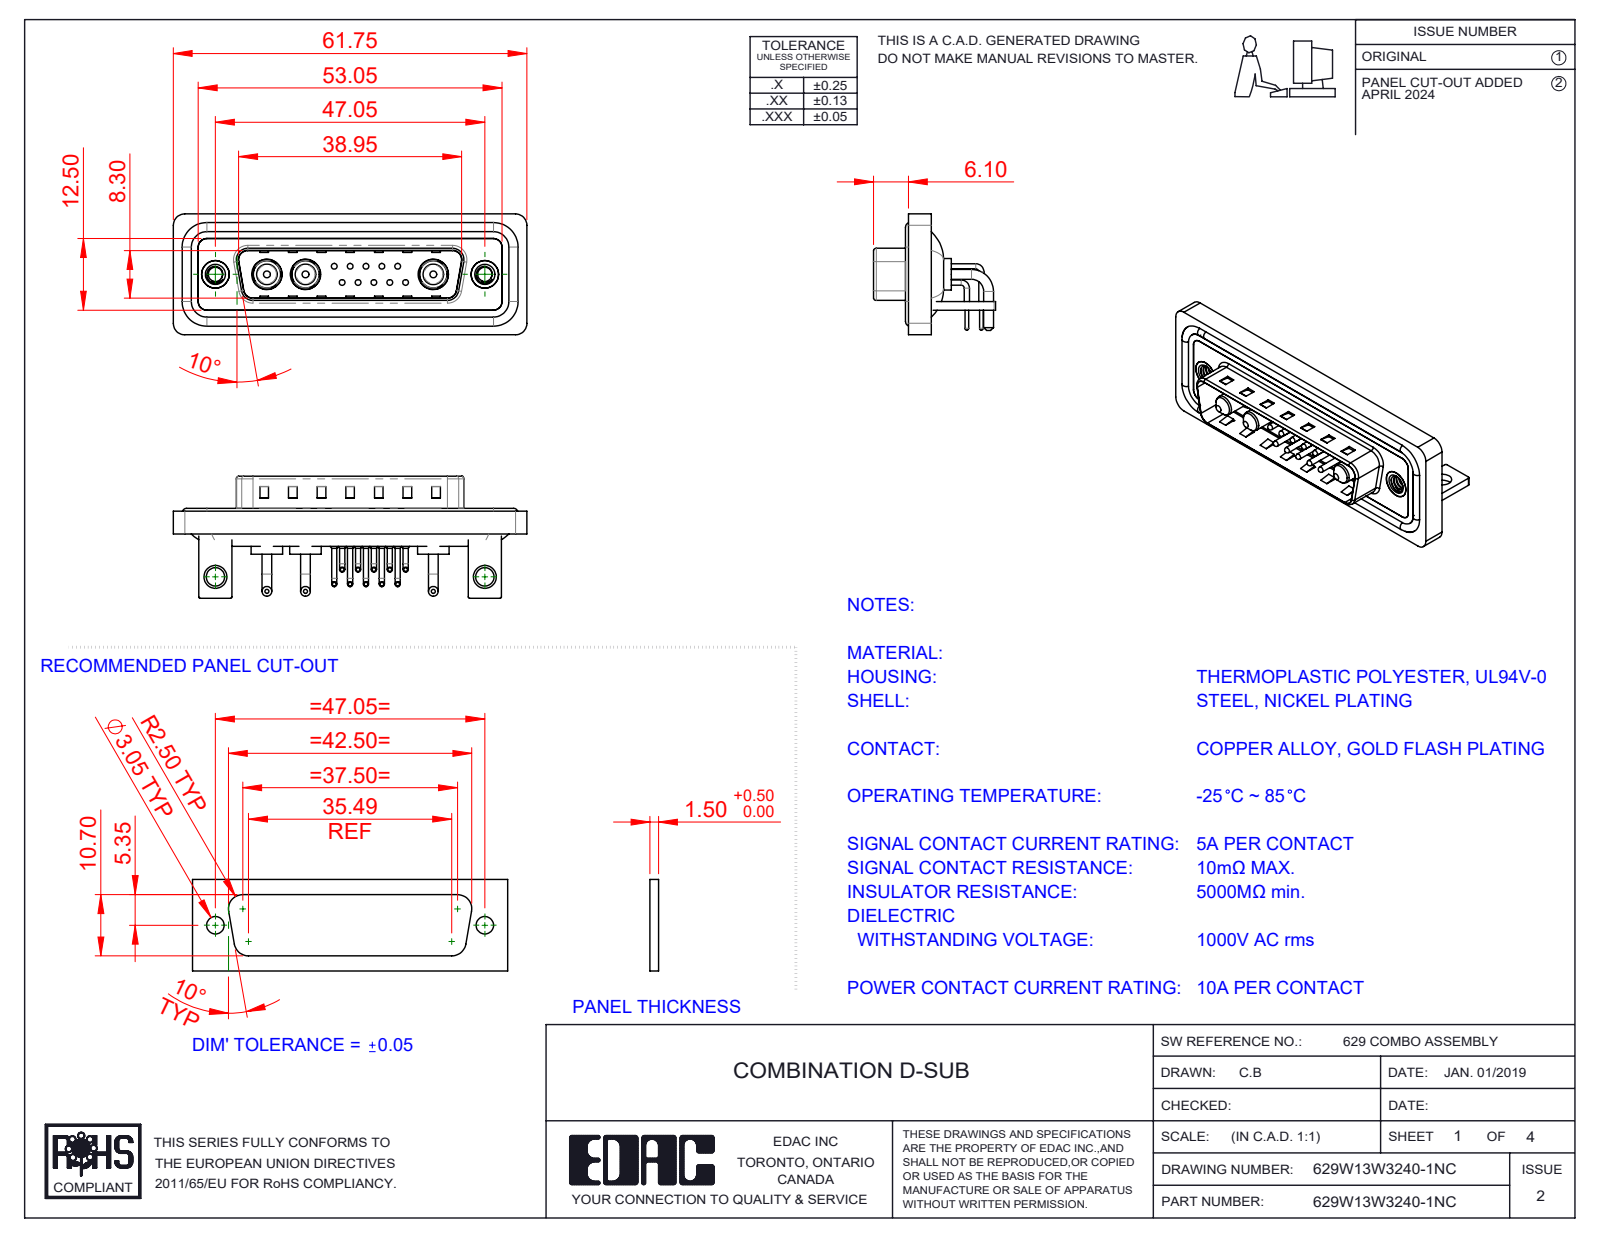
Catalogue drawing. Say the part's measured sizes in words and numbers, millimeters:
The part is named "629Combo Housing_13W3; 629Combo Contact Row 1; 629W13W3240-1NC; 629Combo Stabilizer Bracket (+6 more)". Its 3-D file was written by "SolidWorks 2023 (CONFIG_CONTROL_DESIGN)". It is 25 solids with 1750 faces: 899 planar, 629 cylindrical and 222 other. Overall it measures 61.75 by 21.3 by 21.1 millimeters. Its volume is 7 708 cubic millimeters and its surface area 12 932 square millimeters. Round holes: 10 of diameter 0.75, 10 of diameter 1.6, 10 of diameter 2, 3 of diameter 4.85, 3 of diameter 5.3, 2 of diameter 2.5, 2 of diameter 3.2, 2 of diameter 4, 2 of diameter 4.8, 2 of diameter 5. Round bosses or shafts: 20 of diameter 0.9, 10 of diameter 1.5, 10 of diameter 1, 10 of diameter 0.65, 6 of diameter 1.7, 4 of diameter 1.6, 3 of diameter 5.5, 3 of diameter 5.2. Partial cylindrical surfaces (rounded edges, fillets, slot ends): 19 of radius 2, 18 of radius 1.5, 16 of radius 0.25, 10 of radius 1.01, 9 of radius 0.5, 8 of radius 1.6, 4 of radius 0.6, 4 of radius 0.65. The main face-to-face distances are 0.4, 1.5, 0.8, 2.9, 2.1, 1.1, 4.1, 1.6, 3.7, 4.5. The hole center spacings are 3.16, 2.77, 5.04, 5.54, 7.49, 5.03, 8.31, 10.11.
